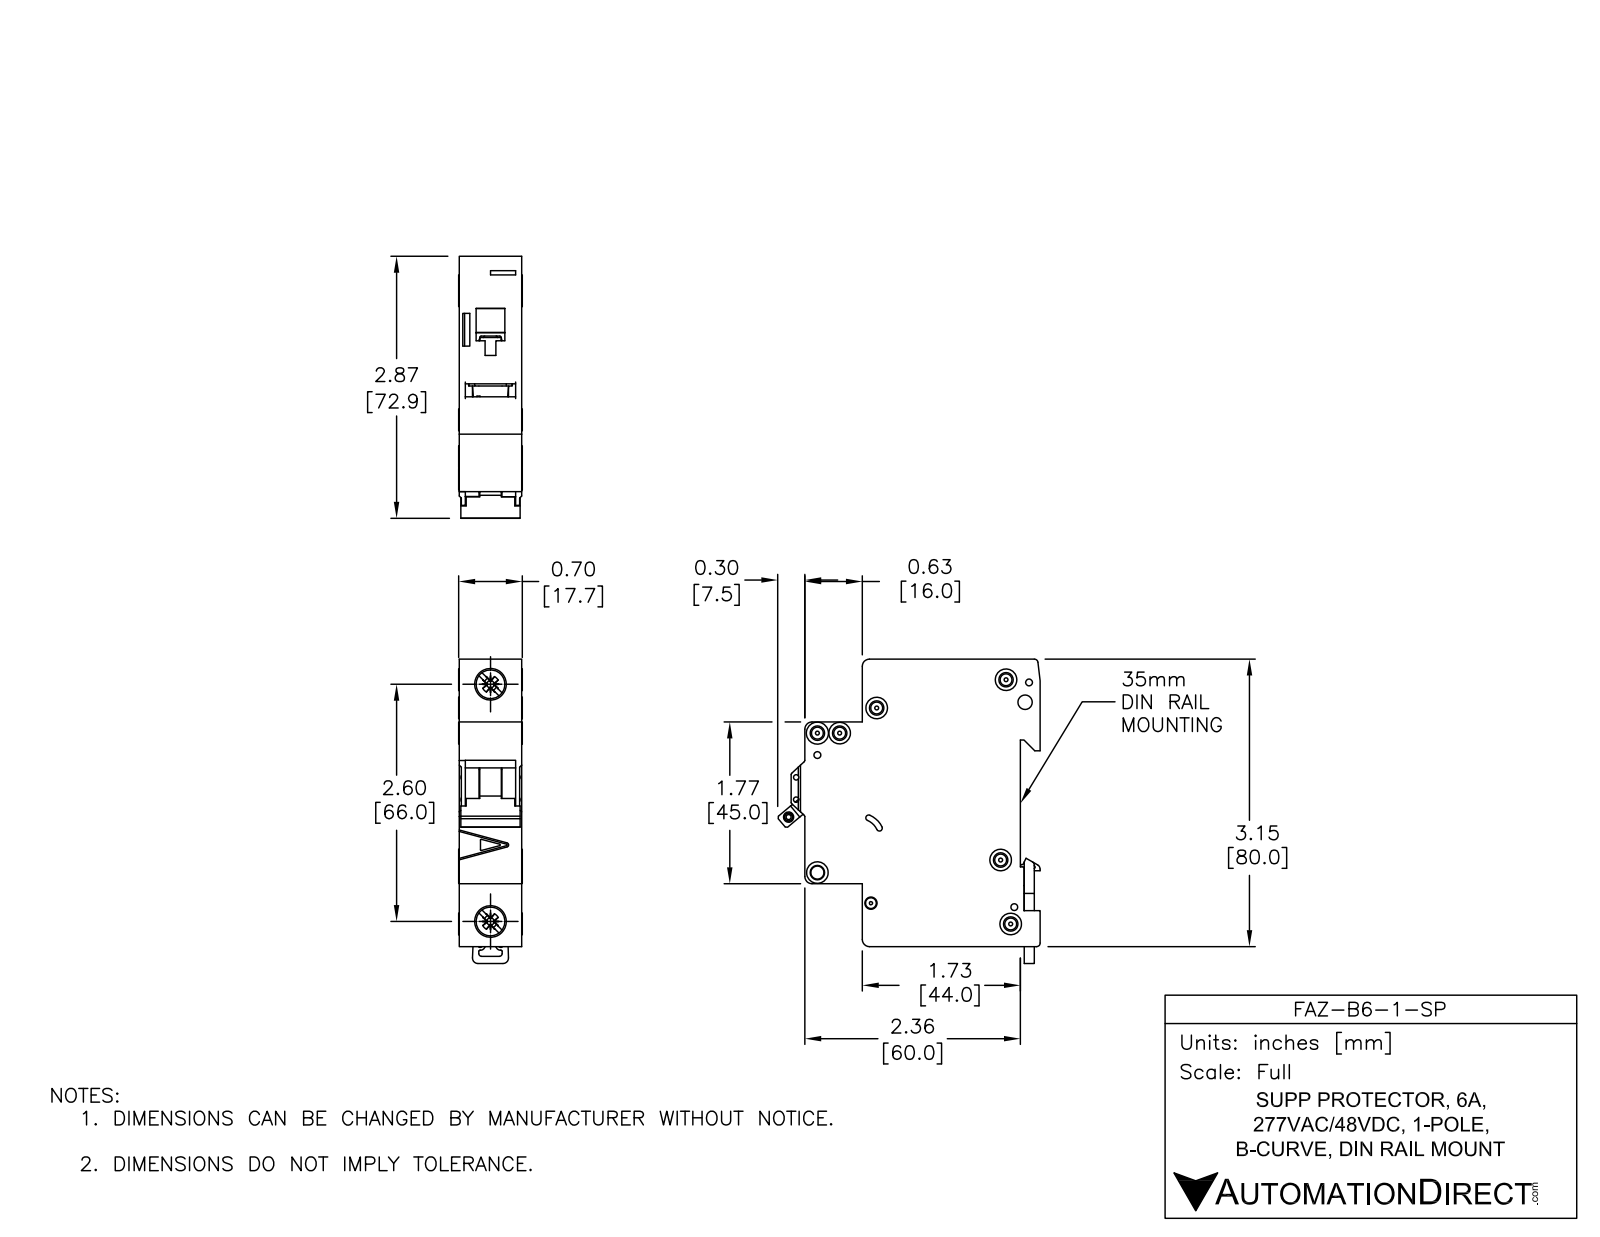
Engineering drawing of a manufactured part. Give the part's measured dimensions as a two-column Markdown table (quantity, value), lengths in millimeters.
| quantity | value |
| --- | --- |
| part name | FAZ-B6-1-SP |
| STEP written by | SolidWorks 2014 (AUTOMOTIVE_DESIGN) |
| units | millimeters |
| bodies | 5 solids, 558 faces (235 planar, 202 cylindrical, 121 other) |
| overall size | 84.78 × 73.04 × 17.7 |
| volume | 74 935 mm³ |
| surface area | 19 545 mm² |
| round holes (diameter × count) | 3.6 × 6, 1.9 × 3, 1.09 × 2, 1.5 × 2, 4 × 2, 7.15 × 2, 2.15 × 1, 2.2 × 1, 2.55 × 1, 3.3 × 1, 3.4 × 1 |
| round bosses / shafts (diameter × count) | 6 × 4, 8.2 × 2, 2.5 × 1 |
| partial cylindrical surfaces (radius × count) | 0.25 × 30, 0.5 × 13, 2 × 8, 0.2 × 5, 1 × 4, 0.8 × 2, 3 × 2, 1.5 × 1 |
| main face-to-face distances | 17.5, 79.48, 5.5, 49.5, 44, 65.5, 60, 16, 1.75, 15.75 |
| hole center spacings | 6.2, 13.64, 4.81, 5.19, 5.61, 6.1, 6.44, 8.19 |
